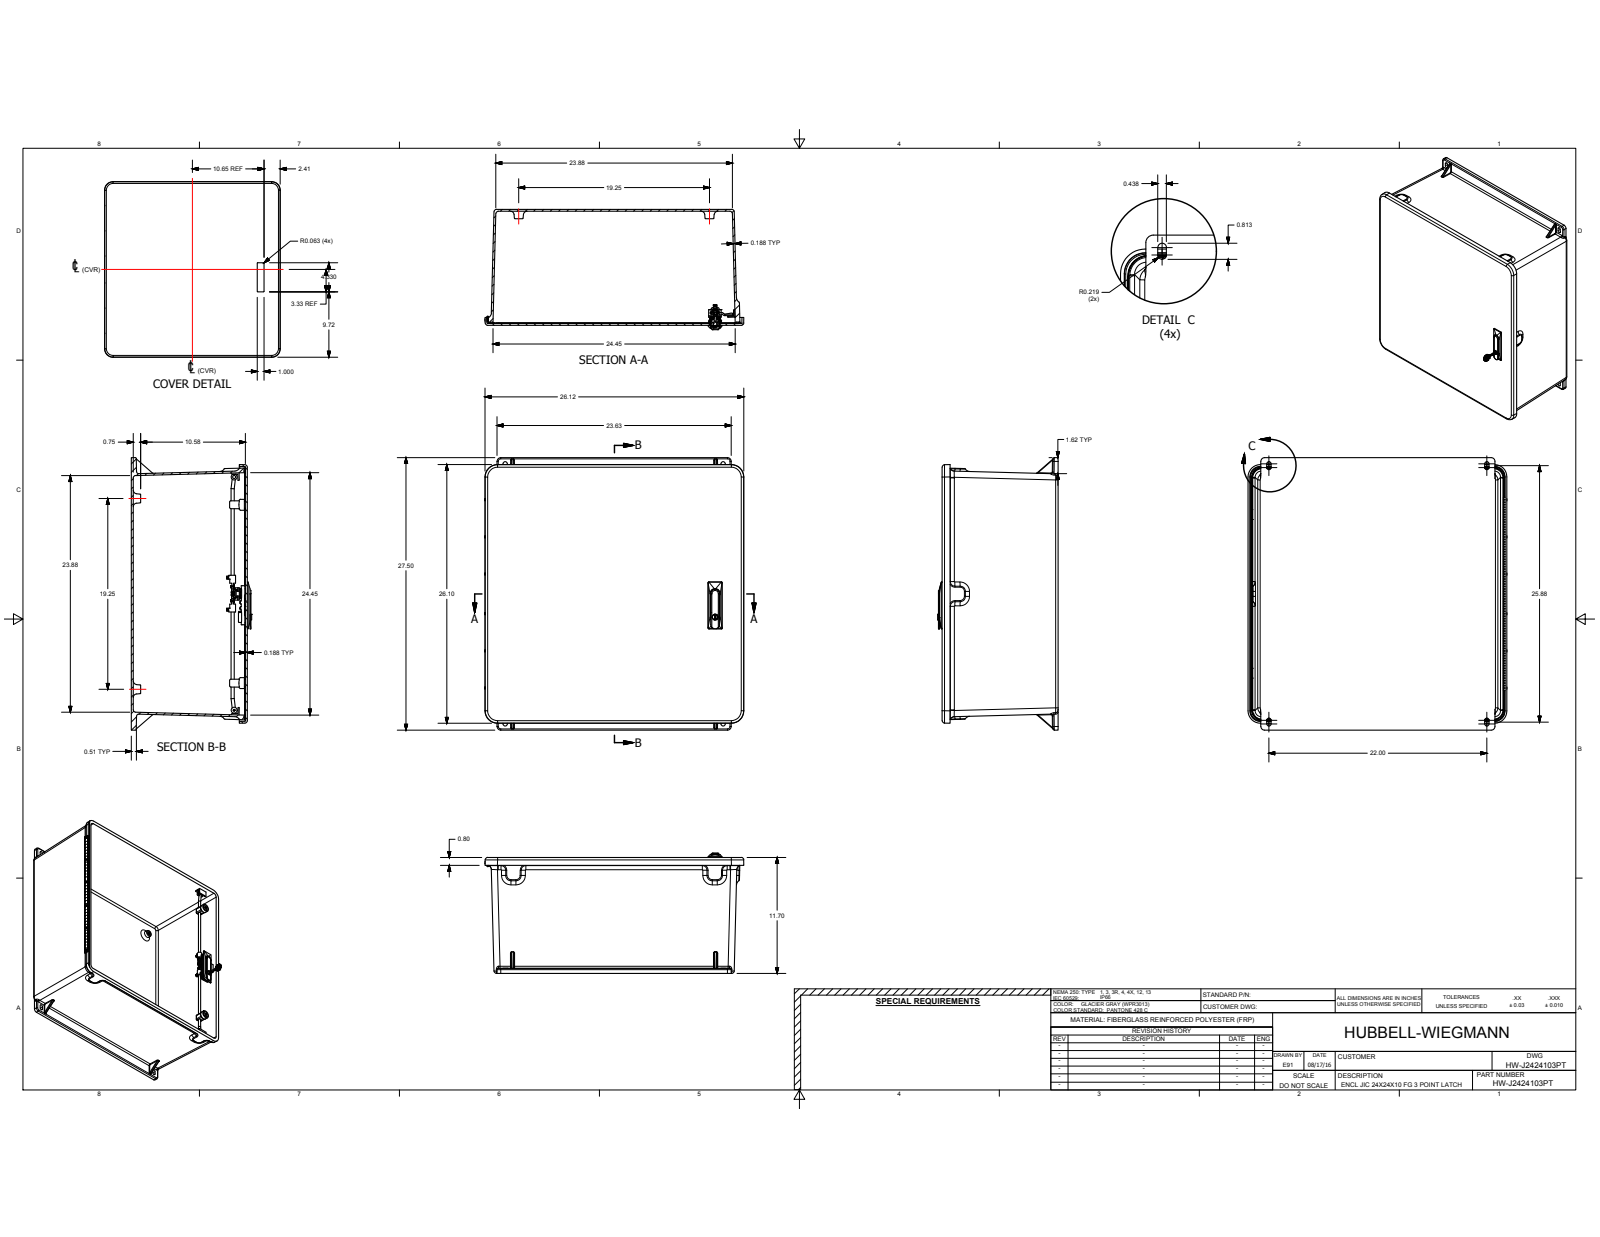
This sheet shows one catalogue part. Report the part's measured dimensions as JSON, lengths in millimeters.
{"part_name": "HW-J2424103PT; WP2424HBOX; WP2424HU3PT; RMGAS_WP2424HCVR (+8 more)", "step_written_by": "Autodesk Inventor 2017 (CONFIG_CONTROL_DESIGN)", "units": "millimeters", "bodies": {"solids": 81, "faces": 5196, "planar": 1685, "cylindrical": 2738, "other": 773}, "overall_size": [698.5, 663.78, 364.65], "volume_mm3": 8720000, "surface_area_mm2": 3459000, "round_holes": [[2.64, 18], [3.33, 12], [3.53, 12], [3.56, 10], [4.2, 4], [5, 4], [5.18, 4], [9.93, 4], [3, 3], [6.2, 3], [2.7, 2], [3.4, 2]], "round_bosses_or_shafts": [[3.17, 18], [8.18, 4], [15, 3], [8, 3], [7.5, 3], [6, 3], [4, 3], [28, 2]], "partial_cylinders_radius": [[0.5, 155], [0.13, 72], [0.3, 43], [1, 36], [0.51, 35], [3.17, 24], [2, 21], [0.55, 20]], "face_to_face_distances": [4.78, 292.43, 297.21, 287.65, 4.77, 641.65, 12.04, 1.9, 290.53, 285.75], "hole_center_spacings": [95.25, 190.5, 279.4, 292.1, 0.34, 184.15, 196.85, 374.65]}
